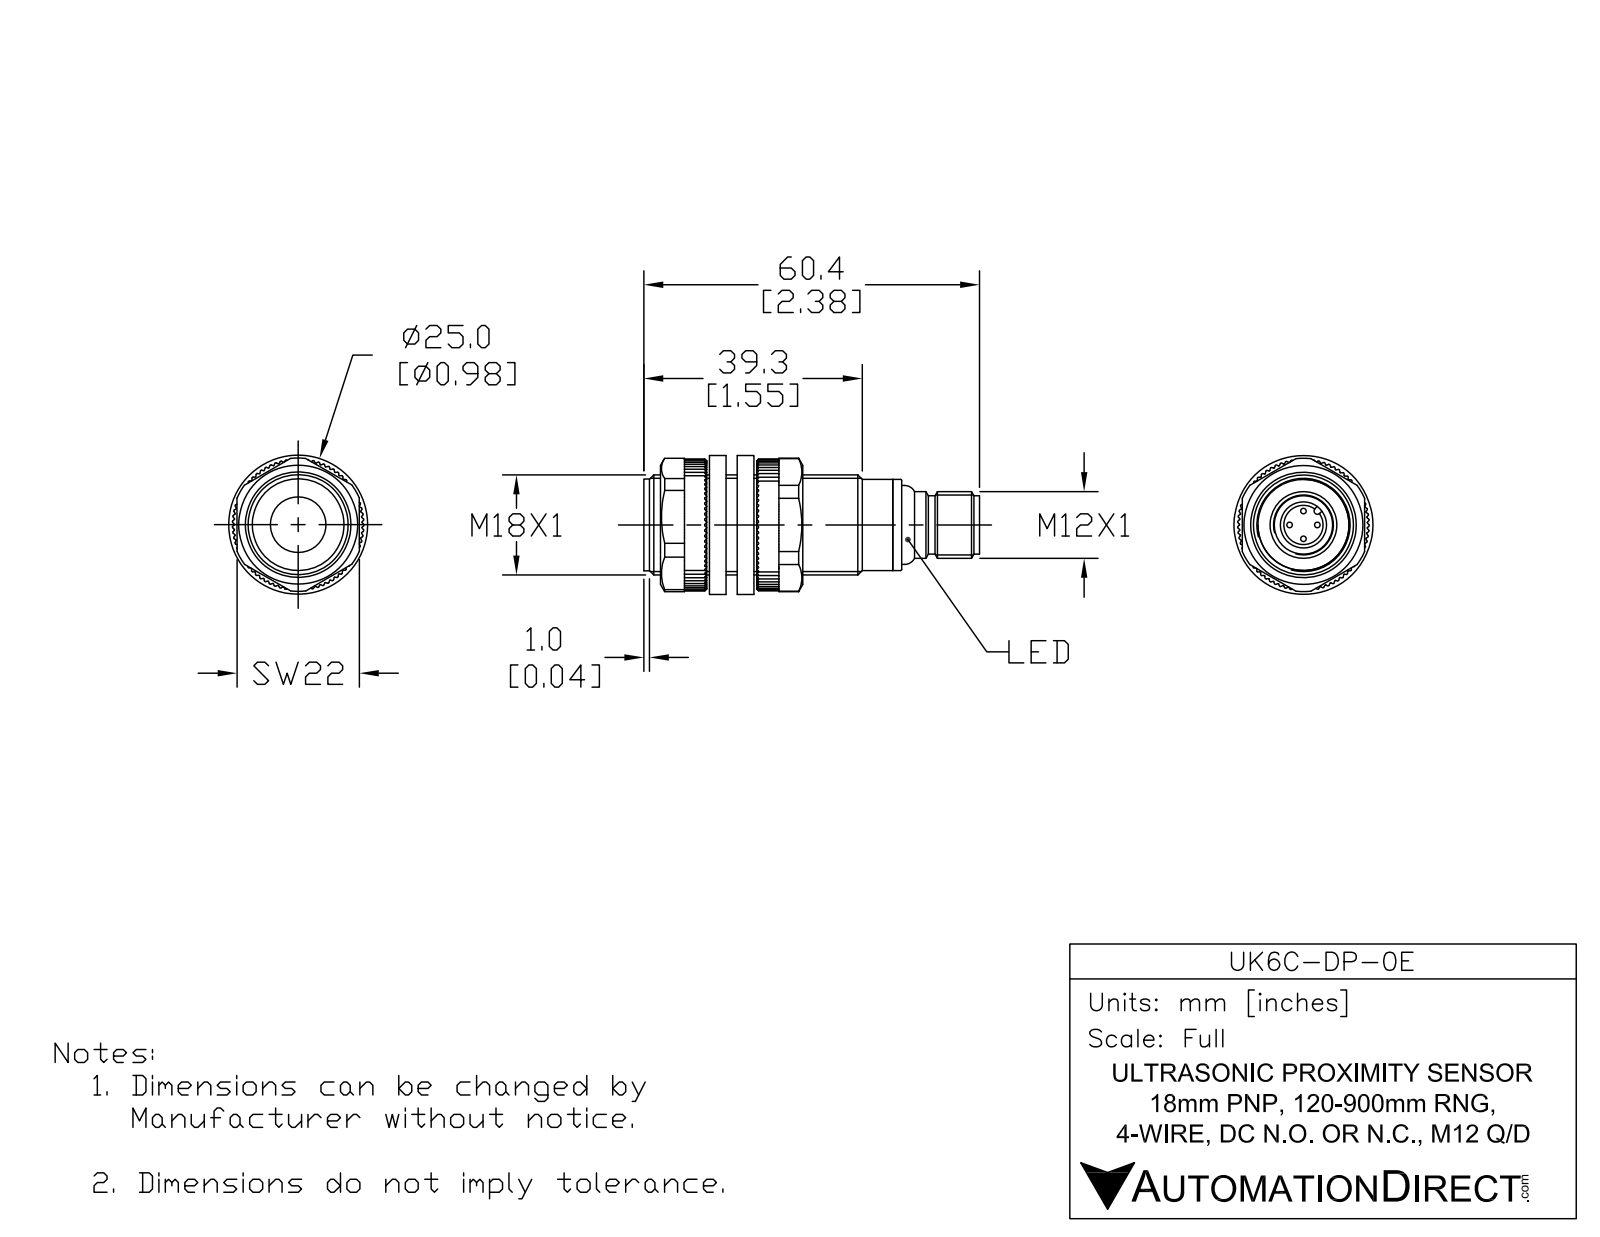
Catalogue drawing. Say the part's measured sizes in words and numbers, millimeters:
The part is named "UK6C-DP-0E". Its 3-D file was written by "SolidWorks 2017 (AUTOMOTIVE_DESIGN)". It is 4 solids with 86 faces: 15 planar, 36 cylindrical and 35 other. Overall it measures 60.3 by 18 by 18 millimeters. Its volume is 12 400 cubic millimeters and its surface area 4 934 square millimeters. Round holes: 1 of diameter 7, 1 of diameter 8.3, 1 of diameter 9.5. Round bosses or shafts: 4 of diameter 1, 1 of diameter 18, 1 of diameter 16.4, 1 of diameter 15.8, 1 of diameter 14.2, 1 of diameter 12, 1 of diameter 10.5. Partial cylindrical surfaces (rounded edges, fillets, slot ends): 1 of radius 0.6. The main face-to-face distances are 43.8, 1, 44.8, 1, 44.8, 46.3, 46.3, 45.3, 1.5, 51.4.
